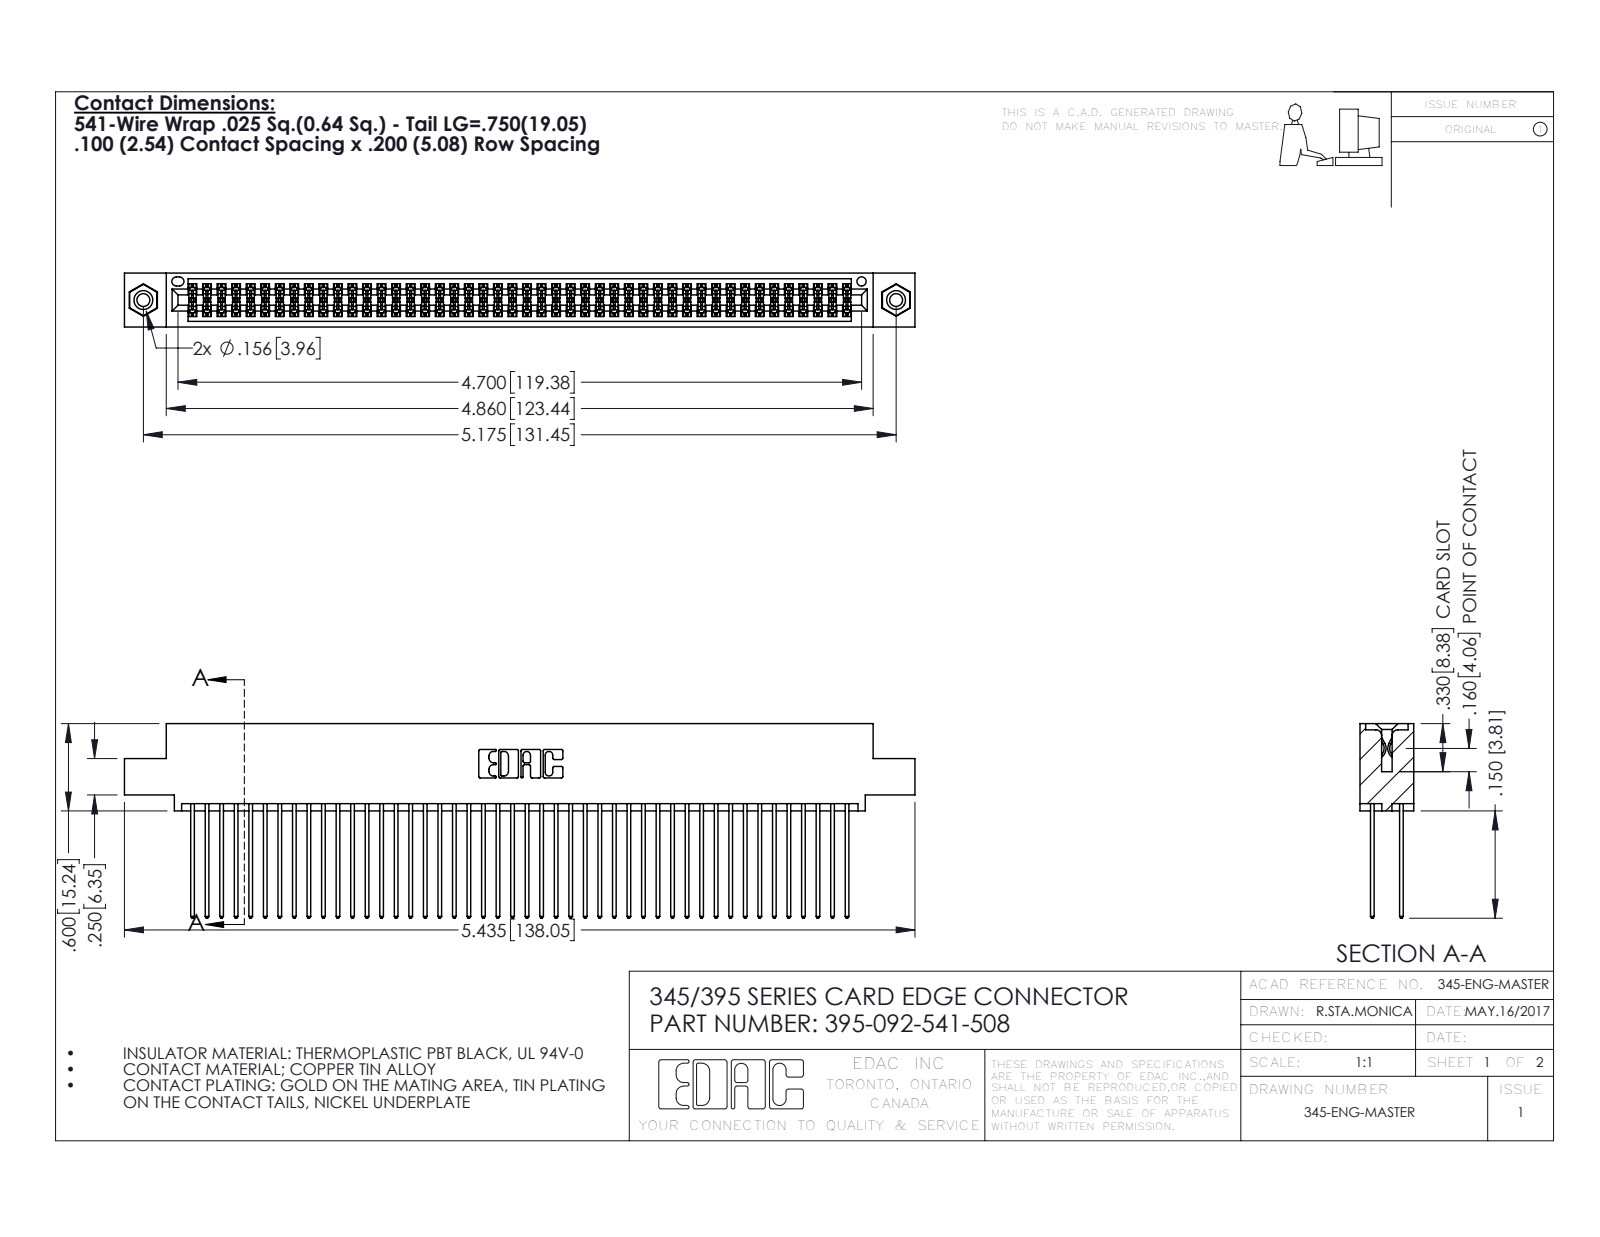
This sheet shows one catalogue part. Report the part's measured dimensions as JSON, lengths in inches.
{"part_name": "345 Part_0.110 Offset - 0.156 Dia-TI; 395-092-541-508; 345-292-001_345-293-141; 345-250-001_345-250-003-102", "step_written_by": "SolidWorks 2016 (CONFIG_CONTROL_DESIGN)", "units": "inches", "bodies": {"solids": 95, "faces": 4790, "planar": 3152, "cylindrical": 1622, "other": 16}, "overall_size": [5.435, 1.337, 0.37], "volume_in3": 0.848, "surface_area_in2": 35.97, "round_holes": [[0.089, 2], [0.125, 2], [0.156, 2], [0.064, 1]], "round_bosses_or_shafts": [[0.155, 2]], "partial_cylinders_radius": [[0.006, 138], [0.01, 92], [0.01, 22], [0.007, 6], [0.031, 6], [0.026, 3], [0.014, 2], [0.019, 2]], "face_to_face_distances": [0.072, 0.298, 0.2, 0.098, 0.272, 0.025, 0.225, 0.37, 0.175, 0.149], "hole_center_spacings": [0.27, 4.939, 5.175]}
